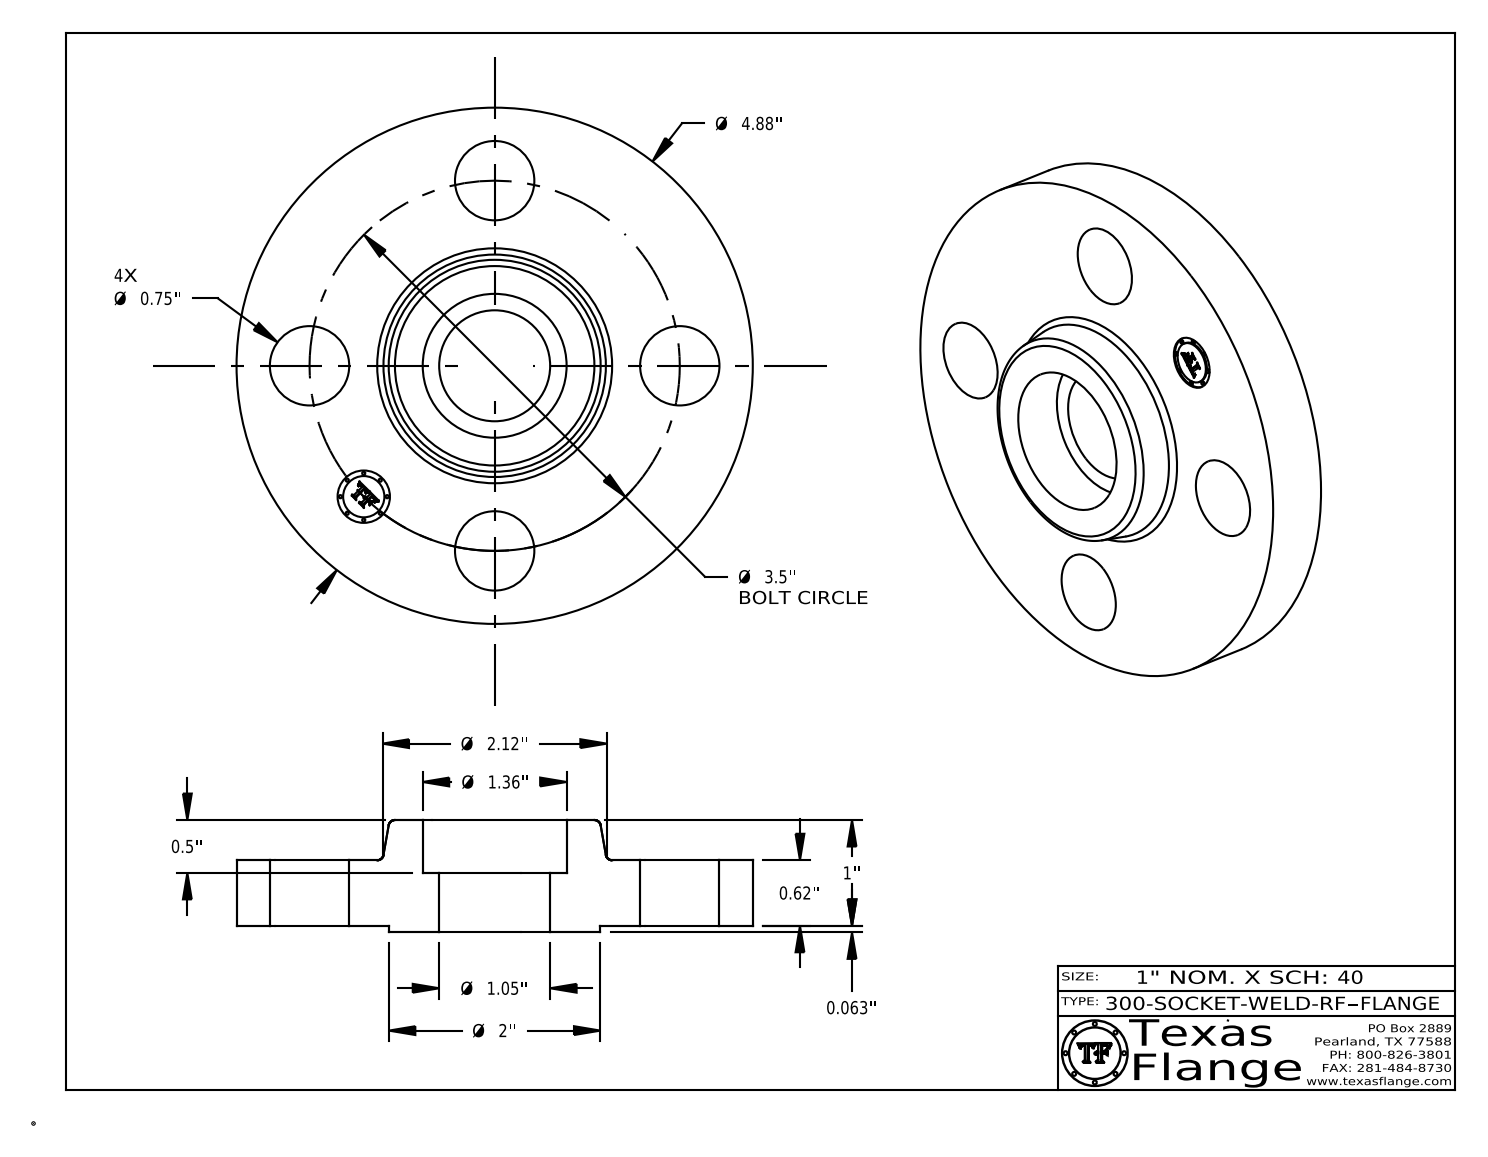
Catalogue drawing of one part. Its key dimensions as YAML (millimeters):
part_name: "300-SOCKET-WELD-RF"
step_written_by: "CATIA V5 STEP AP214 (AUTOMOTIVE_DESIGN)"
units: millimeters
bodies: {solids: 1, faces: 412, planar: 370, cylindrical: 36, other: 6}
overall_size: [124, 124, 27]
volume: 176000
surface_area: 34720
round_holes:
  - {diameter: 19.1, count: 4}
  - {diameter: 12.6, count: 1}
  - {diameter: 26.6, count: 1}
  - {diameter: 34.5, count: 1}
round_bosses_or_shafts:
  - {diameter: 0.8, count: 8}
  - {diameter: 124, count: 1}
  - {diameter: 50.8, count: 1}
  - {diameter: 9.9, count: 1}
face_to_face_distances: [15.7, 1.6, 17.3, 27, 25.4, 9.7, 12.7, 14.3, 3, 2.7]
hole_center_spacings: [44.5, 62.9, 34, 82.1, 88.9]
